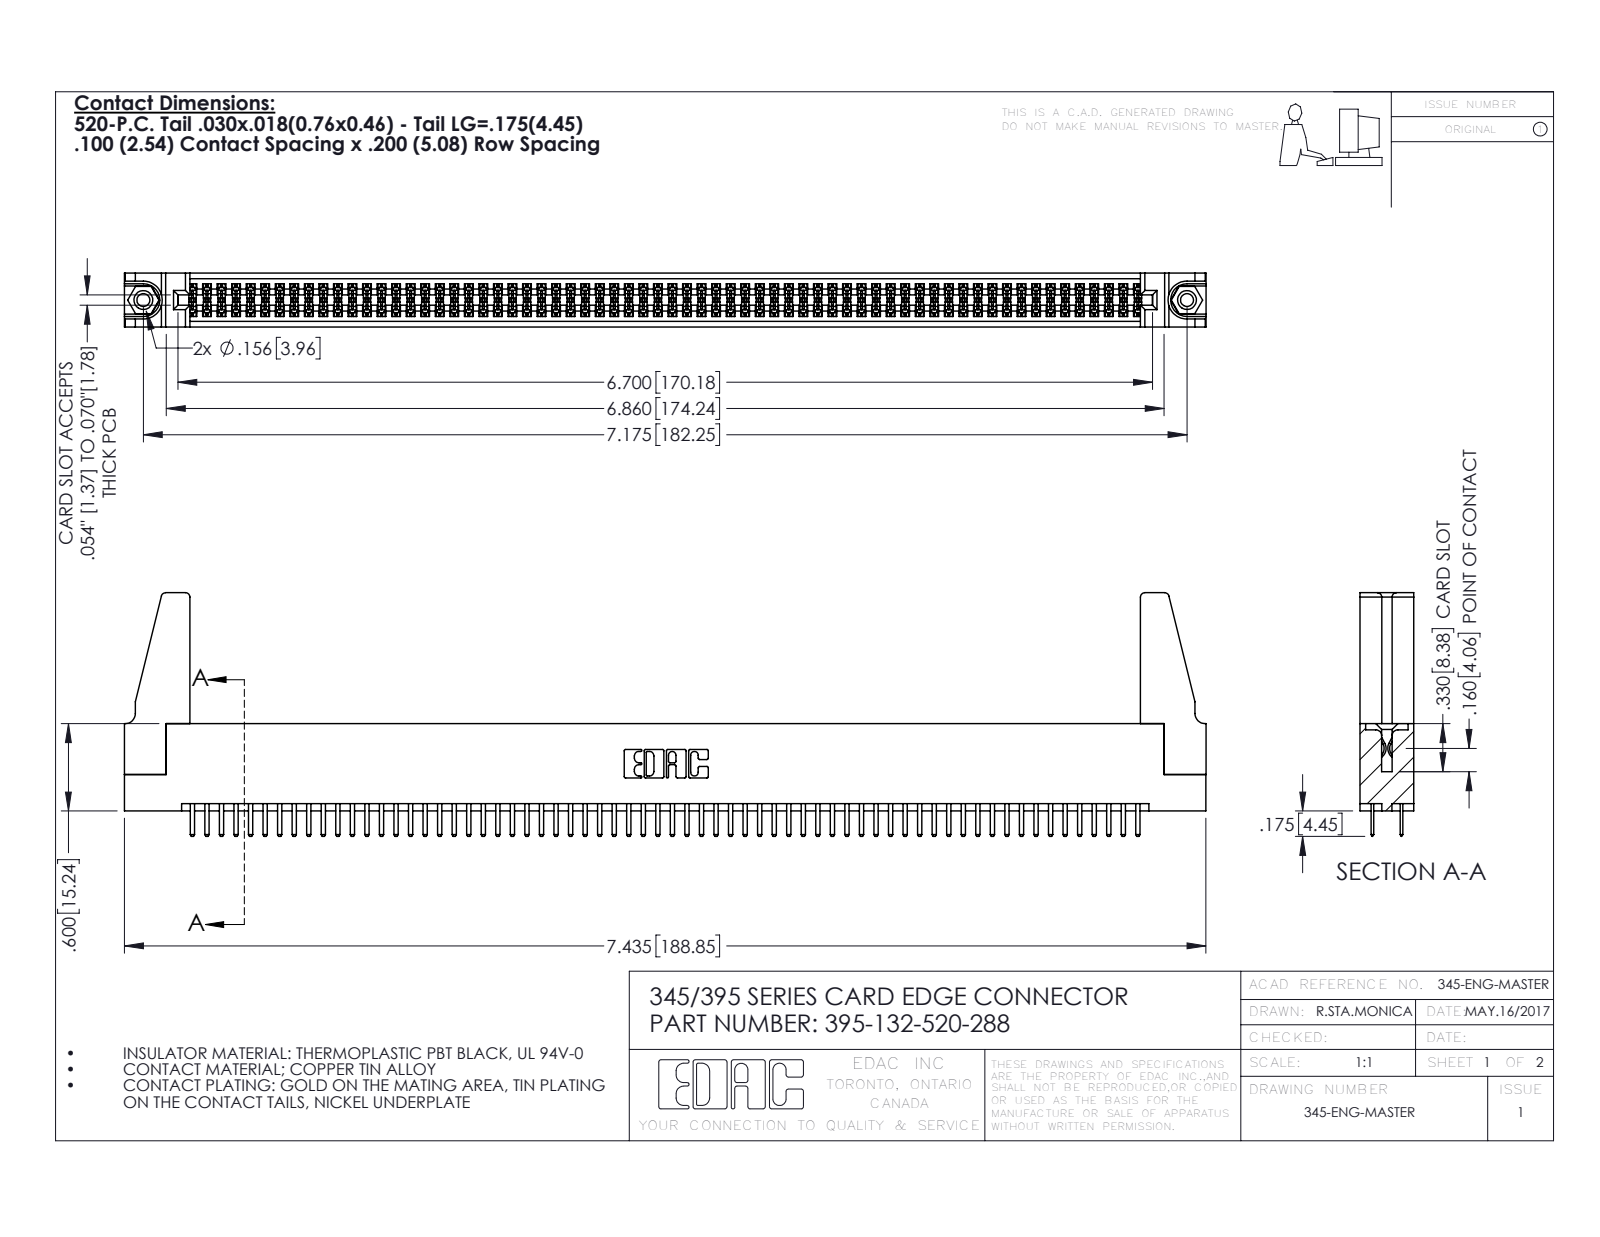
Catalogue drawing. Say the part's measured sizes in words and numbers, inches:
The part is named "345 Part_Flush Mounting Lugs - 0.156 Dia-TH; 395-132-520-288; 345-250-001_345-250-001-102; 345-220-078_345-220-088 (+1 more)". Its 3-D file was written by "SolidWorks 2016 (CONFIG_CONTROL_DESIGN)". It is 137 solids with 7378 faces: 4772 planar, 2590 cylindrical and 16 other. Overall it measures 7.436 by 1.675 by 0.37 inches. Its volume is 1.328 cubic inches and its surface area 47.78 square inches. Round holes: 2 of diameter 0.089, 2 of diameter 0.125, 2 of diameter 0.156, 1 of diameter 0.064. Round bosses or shafts: 2 of diameter 0.155. Partial cylindrical surfaces (rounded edges, fillets, slot ends): 198 of radius 0.006, 136 of radius 0.01, 22 of radius 0.01, 8 of radius 0.03, 6 of radius 0.007, 6 of radius 0.031, 3 of radius 0.026, 2 of radius 0.014. The main face-to-face distances are 0.072, 0.298, 0.37, 0.2, 0.098, 0.272, 0.025, 0.225, 0.022, 0.072. The hole center spacings are 0.27, 6.939, 7.175.
